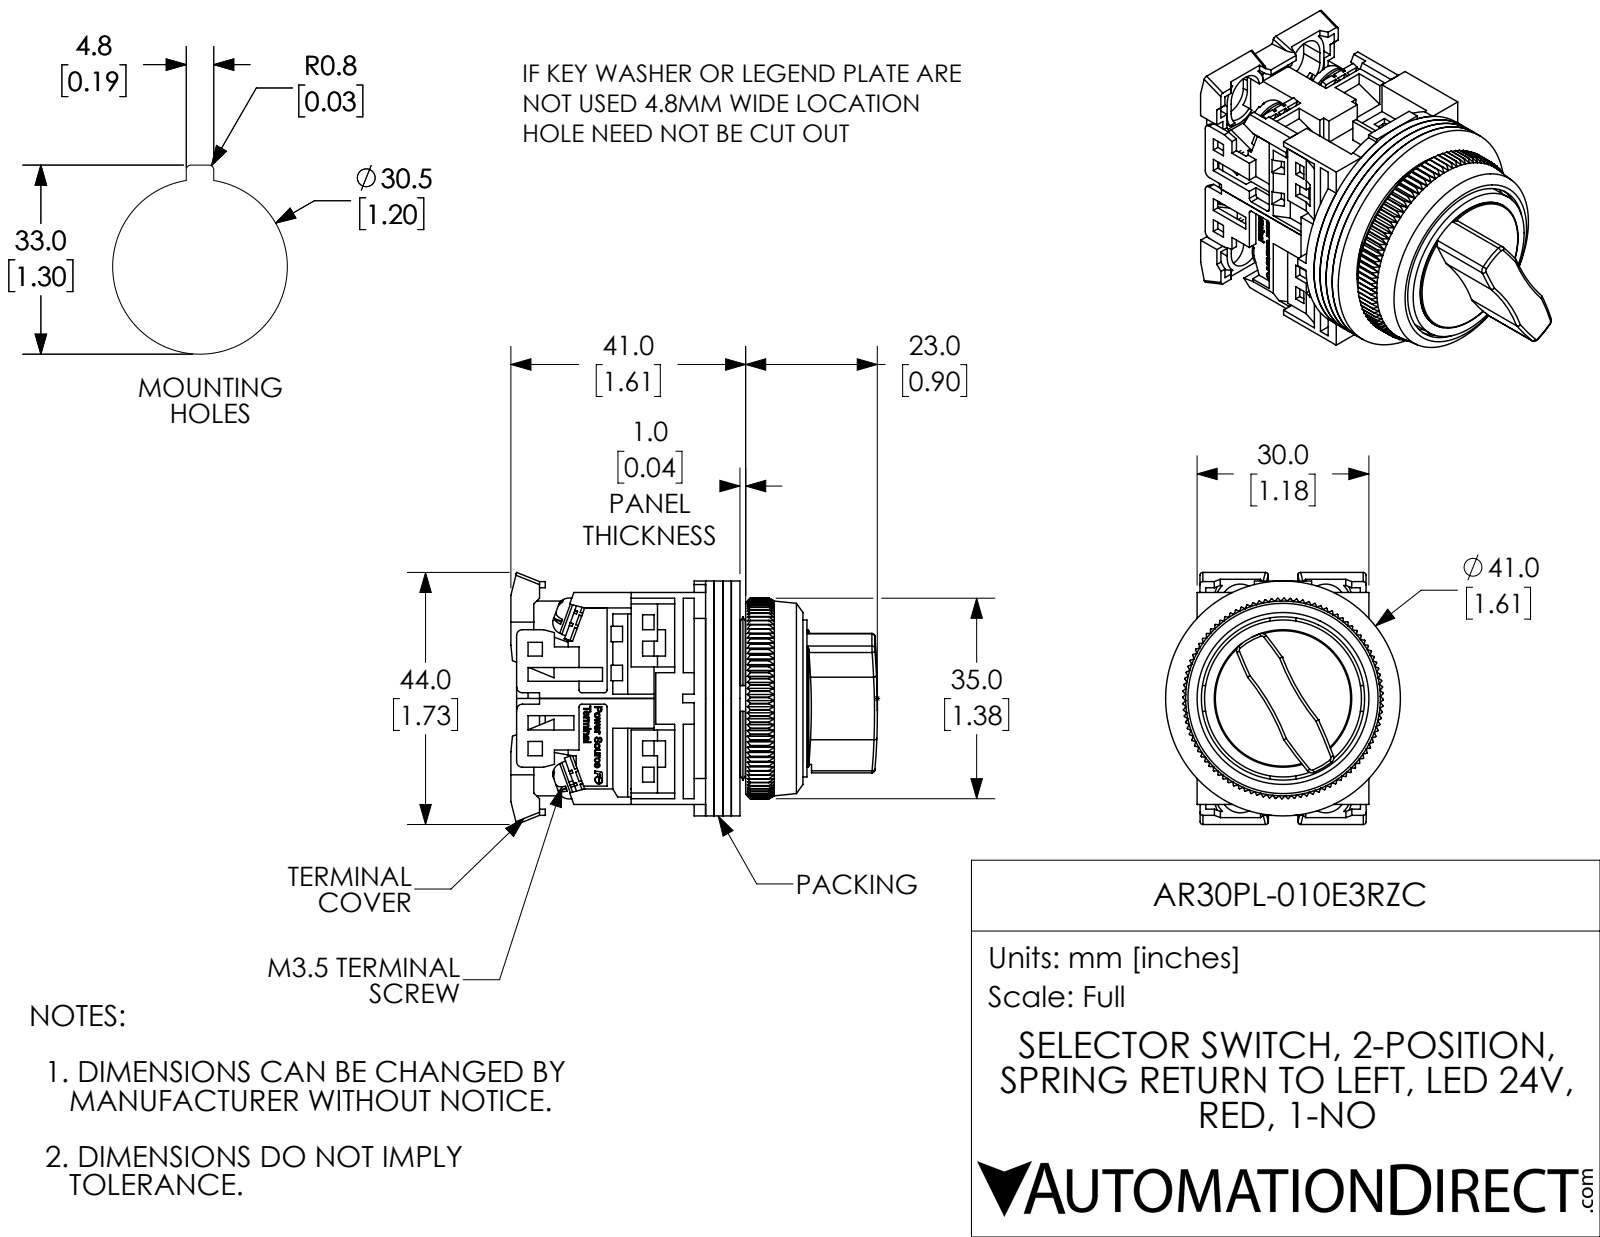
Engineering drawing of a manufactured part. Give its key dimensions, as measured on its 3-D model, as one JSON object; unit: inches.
{"part_name": "AR30PL-010E3RZC", "step_written_by": "SolidWorks 2017 (AUTOMOTIVE_DESIGN)", "units": "inches", "bodies": {"solids": 25, "faces": 2434, "planar": 1731, "cylindrical": 305, "other": 398}, "overall_size": [2.52, 1.732, 1.614], "volume_in3": 2.238, "surface_area_in2": 59.31, "round_holes": [[0.138, 8], [0.142, 4], [0.118, 1], [0.472, 1], [0.709, 1], [0.768, 1], [0.827, 1], [1.122, 1], [1.181, 1], [1.252, 1]], "round_bosses_or_shafts": [[0.26, 4], [0.138, 4], [0.063, 2], [1.614, 1], [1.15, 1], [1.079, 1], [0.945, 1], [0.886, 1]], "partial_cylinders_radius": [[0.059, 16], [0.02, 12], [0.039, 8], [0.138, 4], [0.177, 4], [0.118, 2], [1.575, 2], [2.953, 2]], "face_to_face_distances": [0.059, 0.118, 0.177, 0.039, 0.079, 1.417, 1.358, 0.811, 0.197, 0.02], "hole_center_spacings": [0.579, 0.61]}
